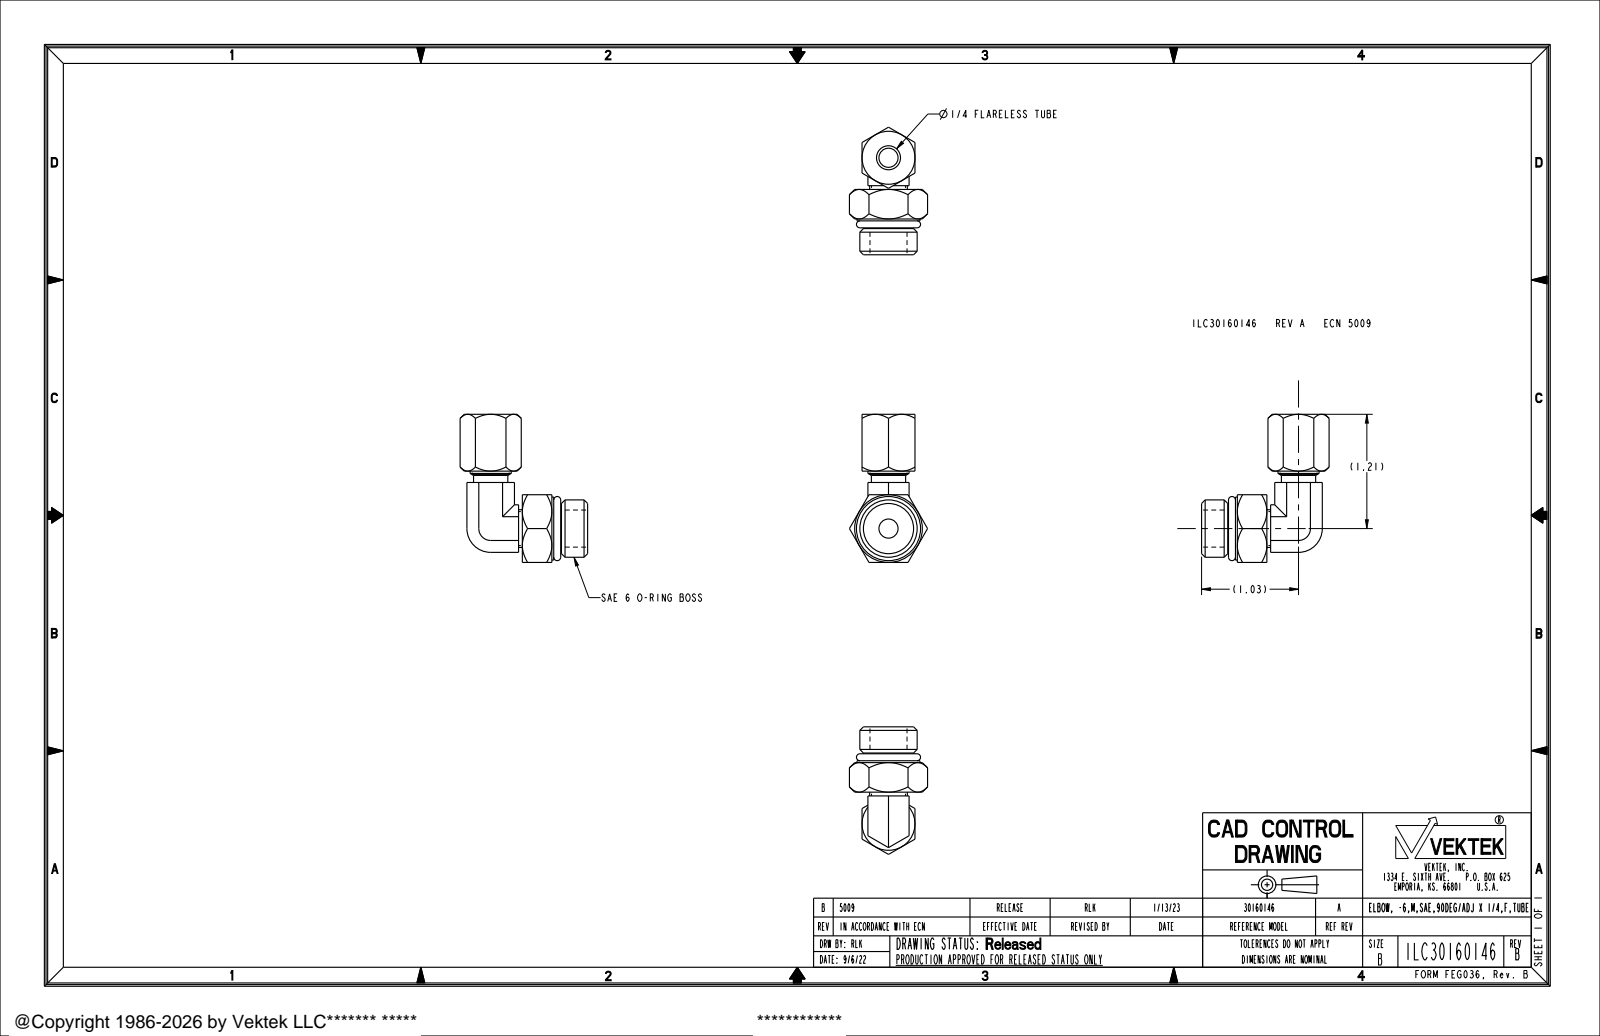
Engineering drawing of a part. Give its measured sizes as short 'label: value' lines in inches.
name: ILC30160146
written by: CREO PARAMETRIC BY PTC INC, 2021164 (AUTOMOTIVE_DESIGN)
unit: in
bodies: 2 solids, 95 faces (33 planar, 26 cylindrical, 36 other)
size: 1.573 × 1.355 × 0.83
volume: 0.489 in³; area: 7.43 in²
holes: 2× ⌀0.203, 1× ⌀0.255
bosses: 1× ⌀0.669, 1× ⌀0.609, 1× ⌀0.533, 1× ⌀0.437, 1× ⌀0.4, 1× ⌀0.394, 1× ⌀0.393, 1× ⌀0.364
face distances: 0.062, 0.5, 0.562, 0.438, 0.719, 0.694, 0.334, 0.36, 1.573, 0.854
